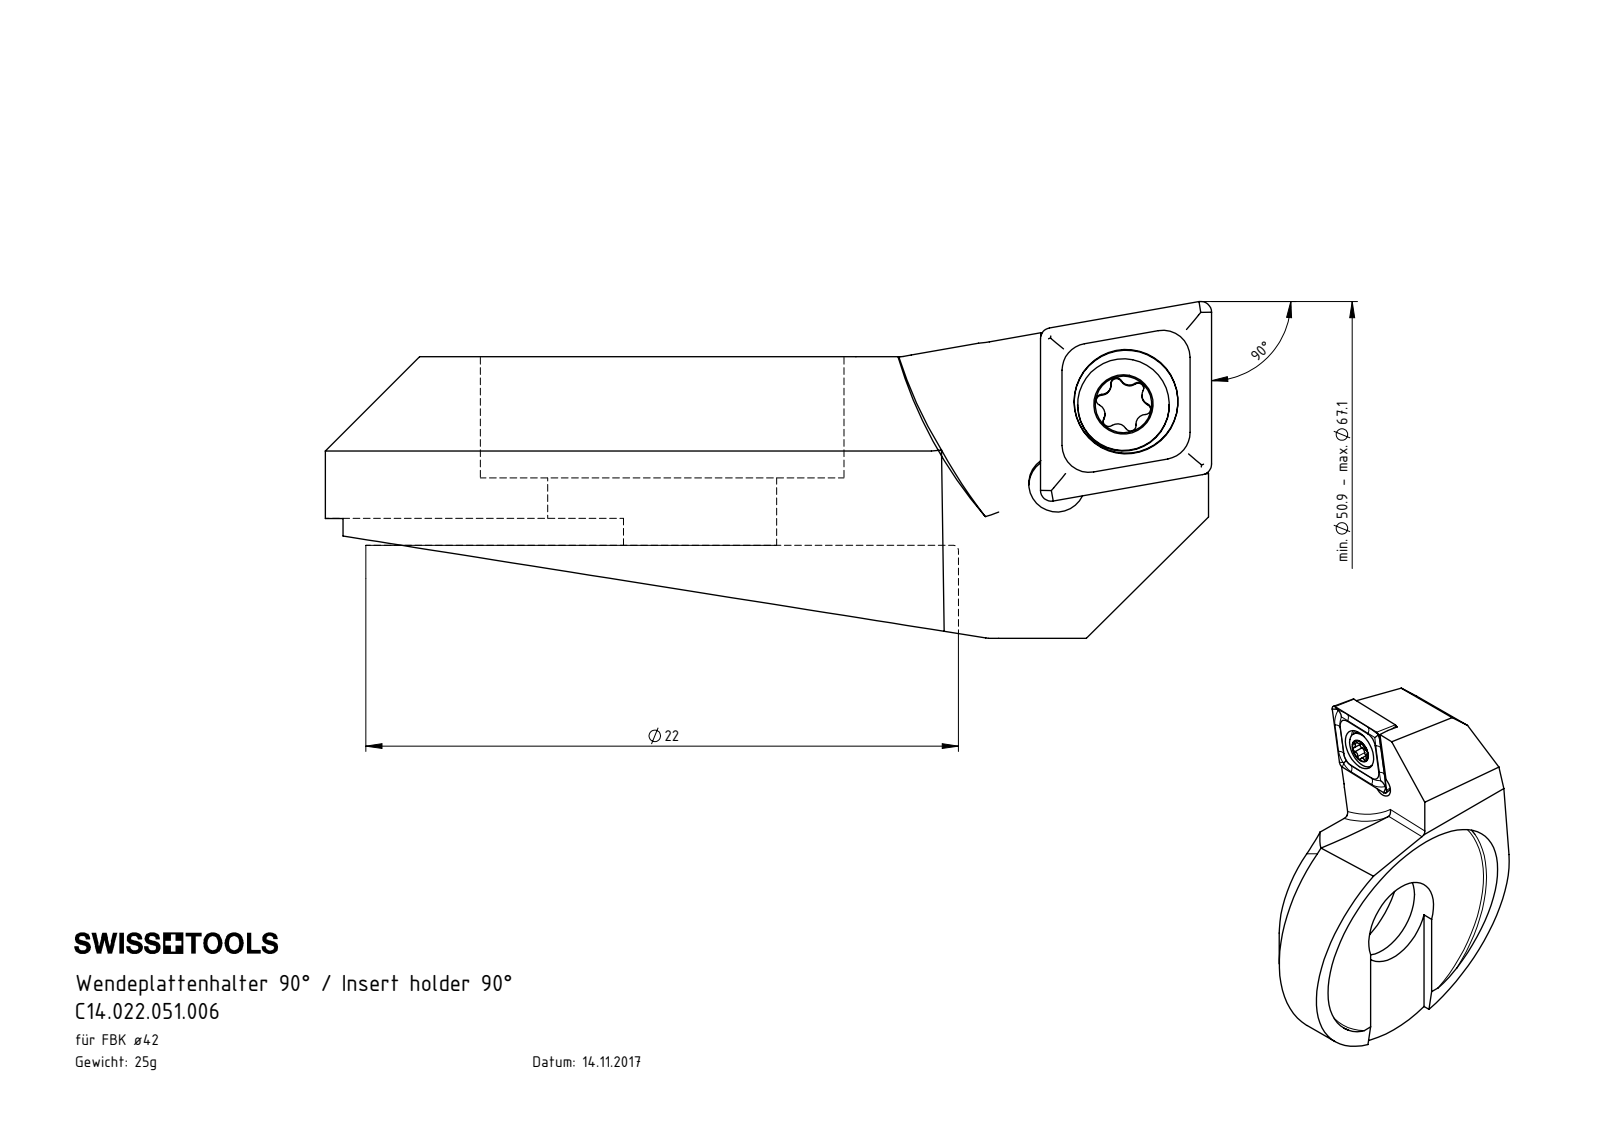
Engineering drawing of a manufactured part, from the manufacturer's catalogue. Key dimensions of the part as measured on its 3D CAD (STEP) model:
Part name (STEP PRODUCT): F42-WCA.001.009_C_fertigbearbeitet; CCMT060204; WCA-ER2.001.006_A; C14.022.051.006
STEP written by: SolidWorks 2017 (CONFIG_CONTROL_DESIGN)
Units: millimetres
Bodies: 5 solids, 147 faces (48 planar, 45 cylindrical, 54 other)
Overall size (bounding box): 32.9 × 25 × 12.5
Volume: 3 269 mm³ · Surface area: 2 741 mm²
Round holes (diameter × count): ⌀2.05 ×1, ⌀2.1 ×1, ⌀2.8 ×1, ⌀3.85 ×1, ⌀8.5 ×1, ⌀13.5 ×1
Round bosses / shafts (diameter × count): ⌀3.4 ×1, ⌀2.5 ×1
Partial cylindrical surfaces — rounded edges, fillets, slot ends (radius × count): R0.21 ×6, R0.36 ×5, R0.5 ×2, R0.36 ×1, R1.05 ×1, R5 ×1, R11 ×1, R12.5 ×1
Main face-to-face distances: 7, 6.7, 2.28, 4.5, 4.2, 2.5, 6, 5.7, 1.5, 1
Hole centre spacings: 3.84, 3.99
